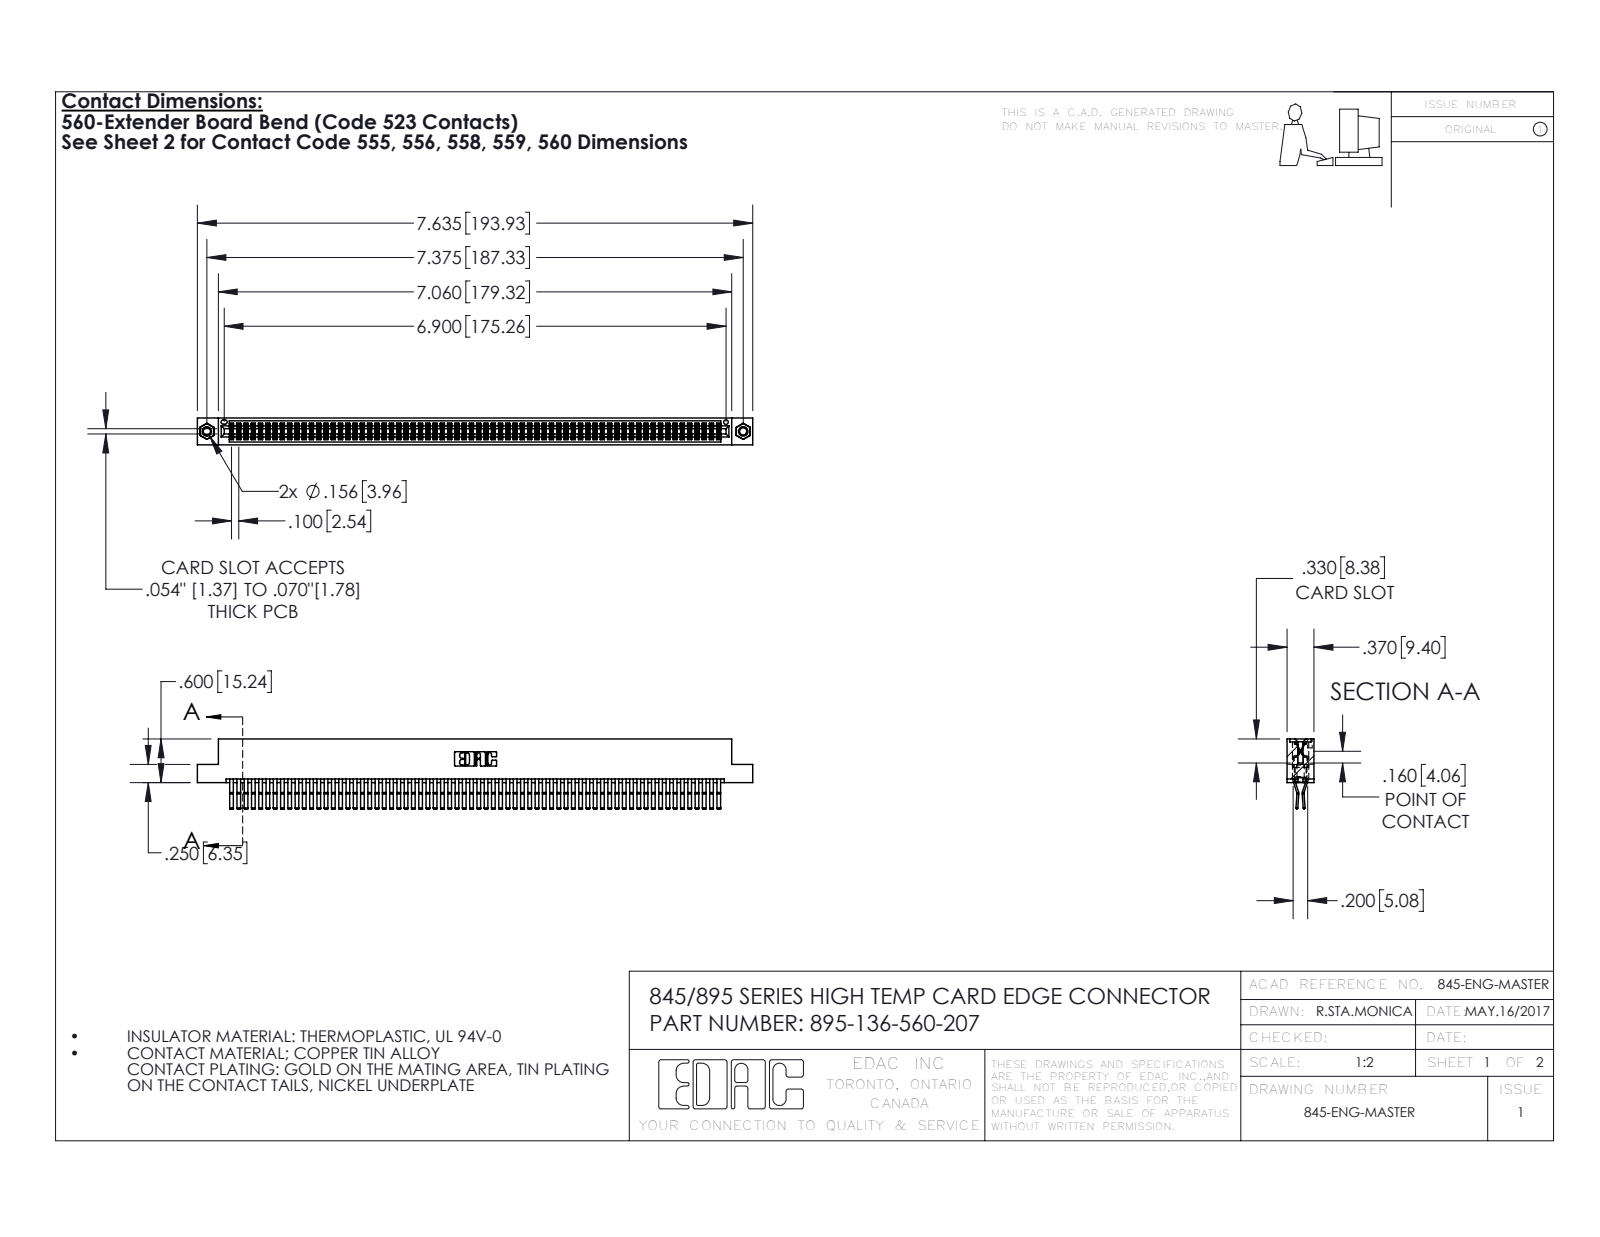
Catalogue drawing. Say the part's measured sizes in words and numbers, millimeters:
The part is named "345 Part_Flush Mounting Lugs - 0.156 Dia-TI; 395-136-560-207; 345-250-001_345-250-005-103; 345-292-001_560 Tail". Its 3-D file was written by "SolidWorks 2016 (CONFIG_CONTROL_DESIGN)". It is 139 solids with 7258 faces: 4600 planar, 2642 cylindrical and 16 other. Overall it measures 193.9 by 24.4 by 9.4 millimeters. Its volume is 19 960 cubic millimeters and its surface area 32 320 square millimeters. Round holes: 2 of diameter 2.5, 2 of diameter 3.2, 2 of diameter 4, 1 of diameter 1.6. Round bosses or shafts: 2 of diameter 3.9. Partial cylindrical surfaces (rounded edges, fillets, slot ends): 204 of radius 0.2, 22 of radius 0.3, 6 of radius 0.2, 6 of radius 0.8, 3 of radius 0.7, 2 of radius 0.3, 2 of radius 0.4, 2 of radius 0.5. The main face-to-face distances are 0.6, 1.8, 7.6, 9.4, 5.1, 2.5, 6.9, 5.7, 4.4, 3.8. The hole center spacings are 6.9, 181.3, 187.3.
